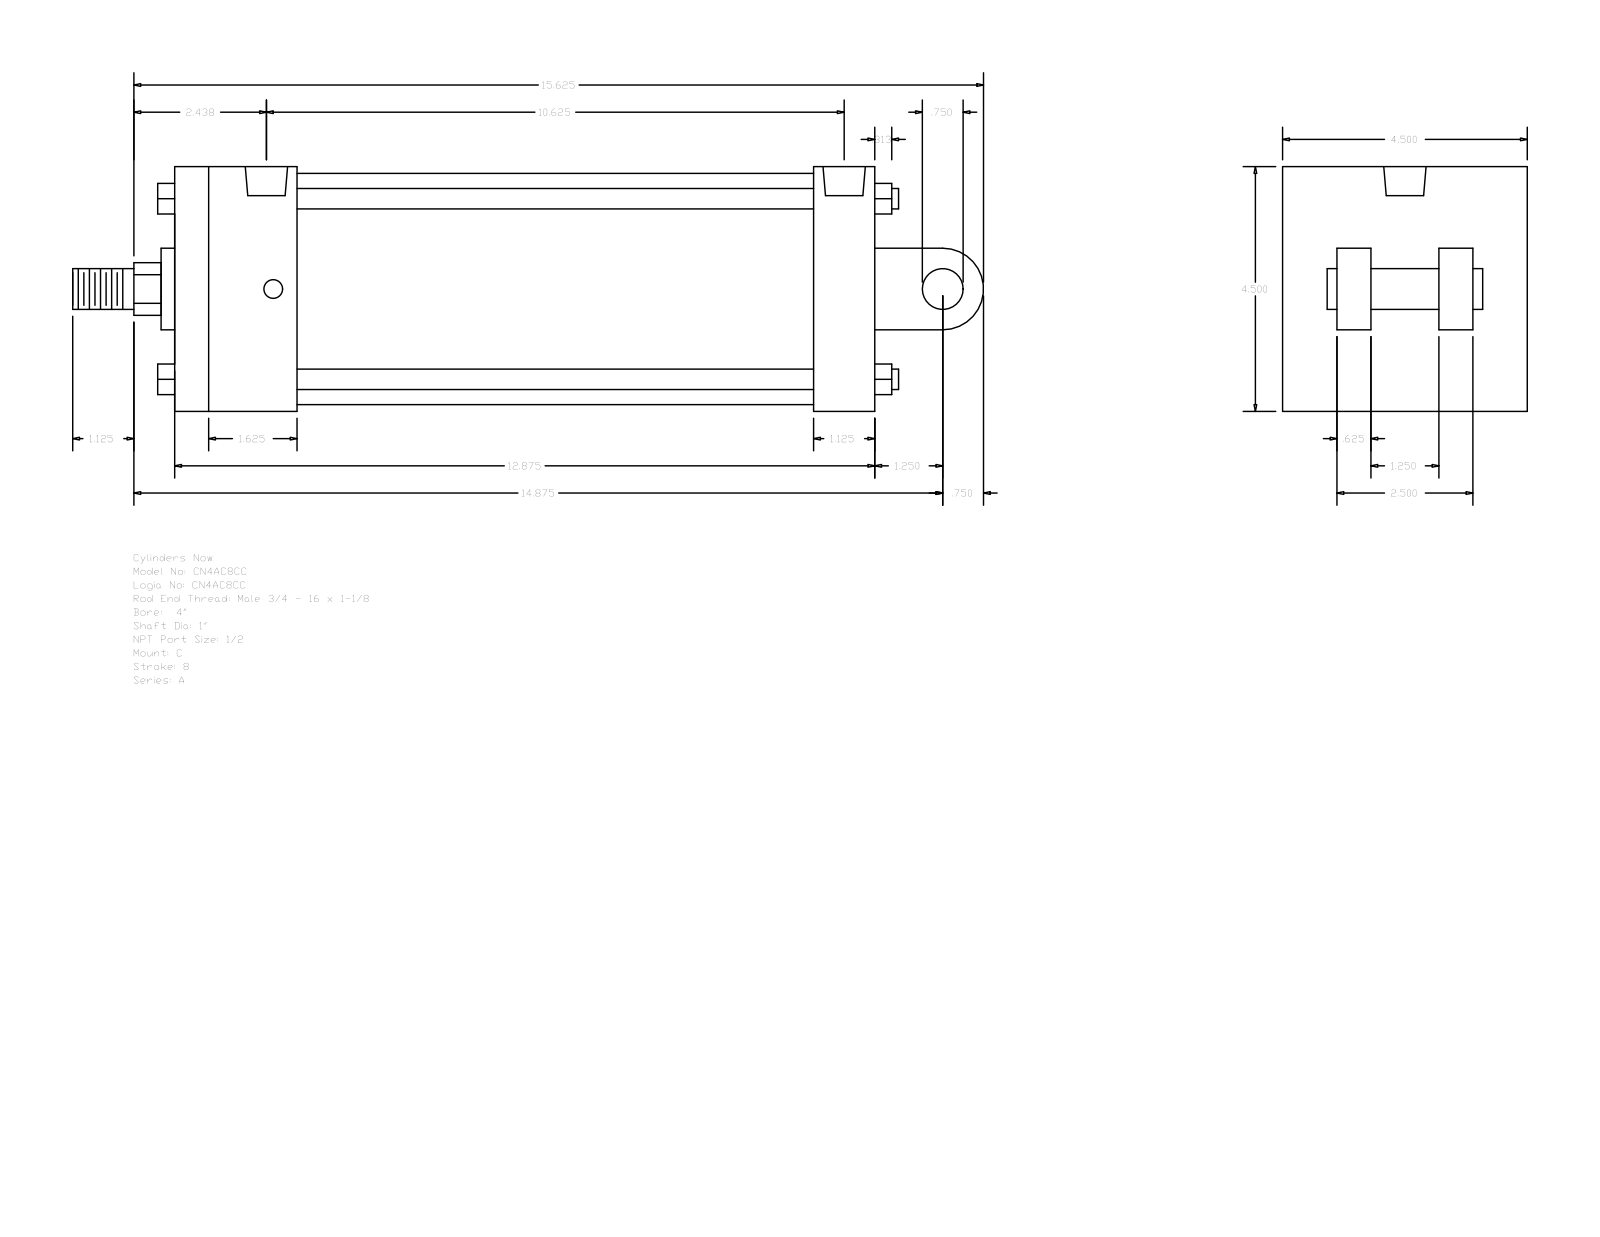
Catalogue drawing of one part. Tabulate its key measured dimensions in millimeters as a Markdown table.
| quantity | value |
| --- | --- |
| part name | A_C__0400_1 |
| STEP written by | GSSL Pune (CONFIG_CONTROL_DESIGN) |
| units | millimeters |
| bodies | 0 solids, 135 faces (102 planar, 33 cylindrical, 0 other) |
| overall size | 425.45 × 114.3 × 114.3 |
| round holes (diameter × count) | 8.73 × 4, 19.77 × 2 |
| round bosses / shafts (diameter × count) | 9.53 × 4, 19.05 × 2, 107.95 × 1, 38.1 × 1, 25.4 × 1 |
| partial cylindrical surfaces (radius × count) | 12.29 × 1, 19.05 × 1 |
| main face-to-face distances | 114.3, 327.02, 73.03, 28.57, 298.45, 57.15, 241.3, 269.87, 41.27, 38.1 |
| hole center spacings | 3.18, 263.52, 266.7, 269.88 |
